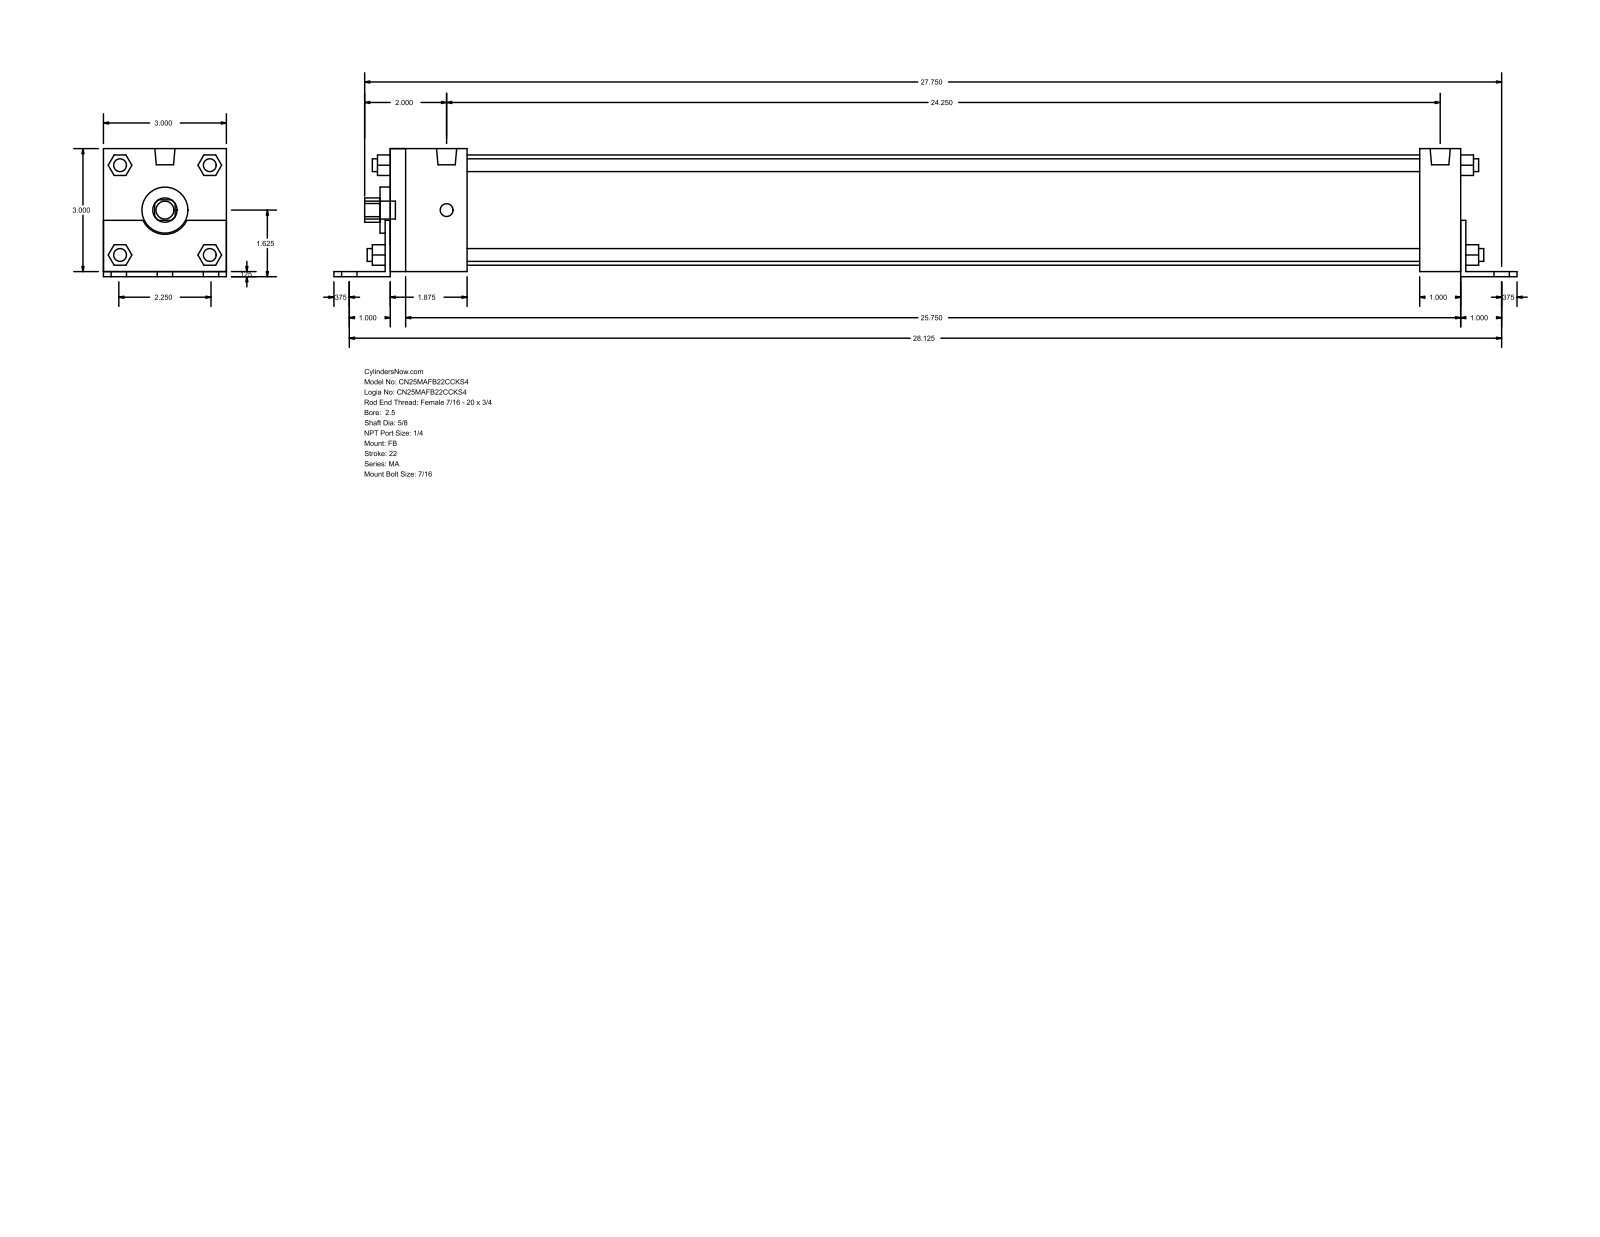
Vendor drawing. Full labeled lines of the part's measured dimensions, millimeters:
Part name (STEP PRODUCT): MA_FB__0250_0.625
STEP written by: GSSL Pune (CONFIG_CONTROL_DESIGN)
Units: millimetres
Bodies: 0 solids, 140 faces (105 planar, 35 cylindrical, 0 other)
Overall size (bounding box): 733.42 × 79.38 × 76.2
Round holes (diameter × count): ⌀15.88 ×1, ⌀28.57 ×1, ⌀68.33 ×1
Round bosses / shafts (diameter × count): ⌀7.94 ×8, ⌀11.11 ×7, ⌀12.49 ×2
Partial cylindrical surfaces — rounded edges, fillets, slot ends (radius × count): R7.54 ×1, R15.05 ×1
Main face-to-face distances: 76.2, 3.17, 79.37, 663.57, 669.92, 3.18, 666.74, 47.62, 25.4, 666.75
